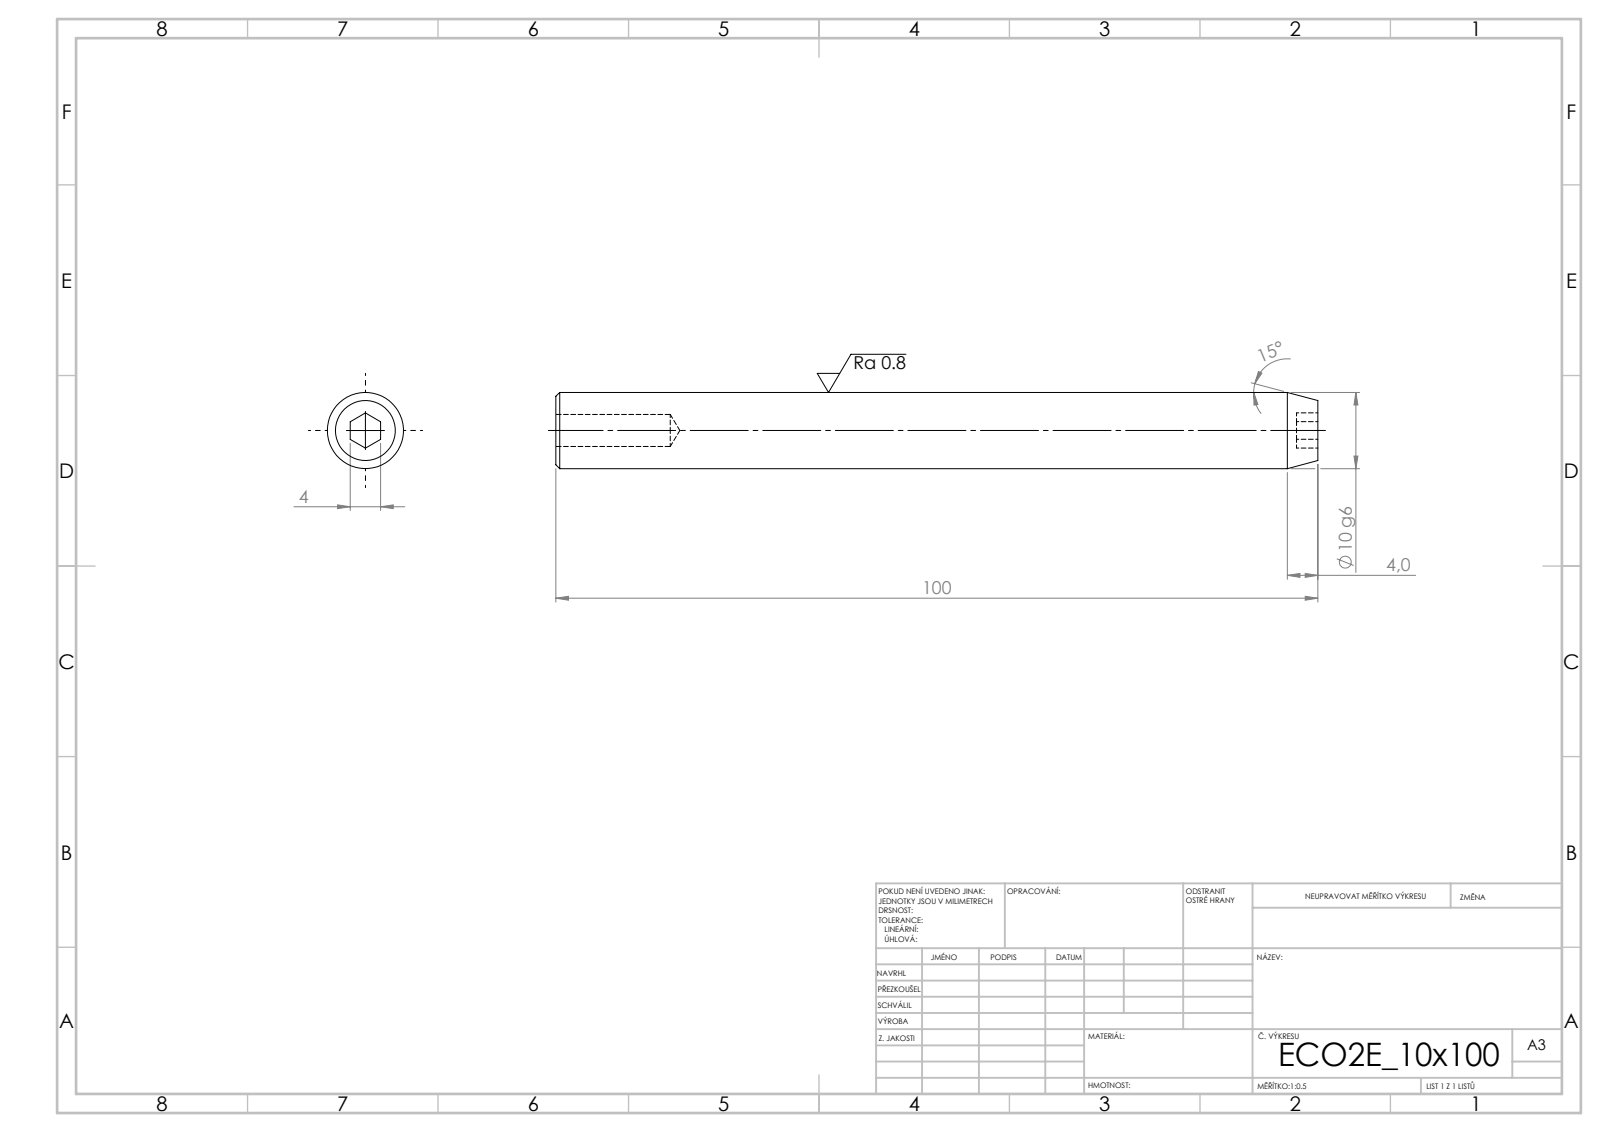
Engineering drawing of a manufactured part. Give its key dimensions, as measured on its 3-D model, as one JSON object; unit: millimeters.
{"step_written_by": "SolidWorks 2019 (CONFIG_CONTROL_DESIGN)", "units": "millimeters", "bodies": {"solids": 1, "faces": 19, "planar": 9, "cylindrical": 4, "other": 6}, "overall_size": [100, 10, 10], "volume_mm3": 7535, "surface_area_mm2": 3489, "round_holes": [[4.2, 1]], "round_bosses_or_shafts": [[10, 1]], "face_to_face_distances": [100, 4, 2.8, 97.2]}
